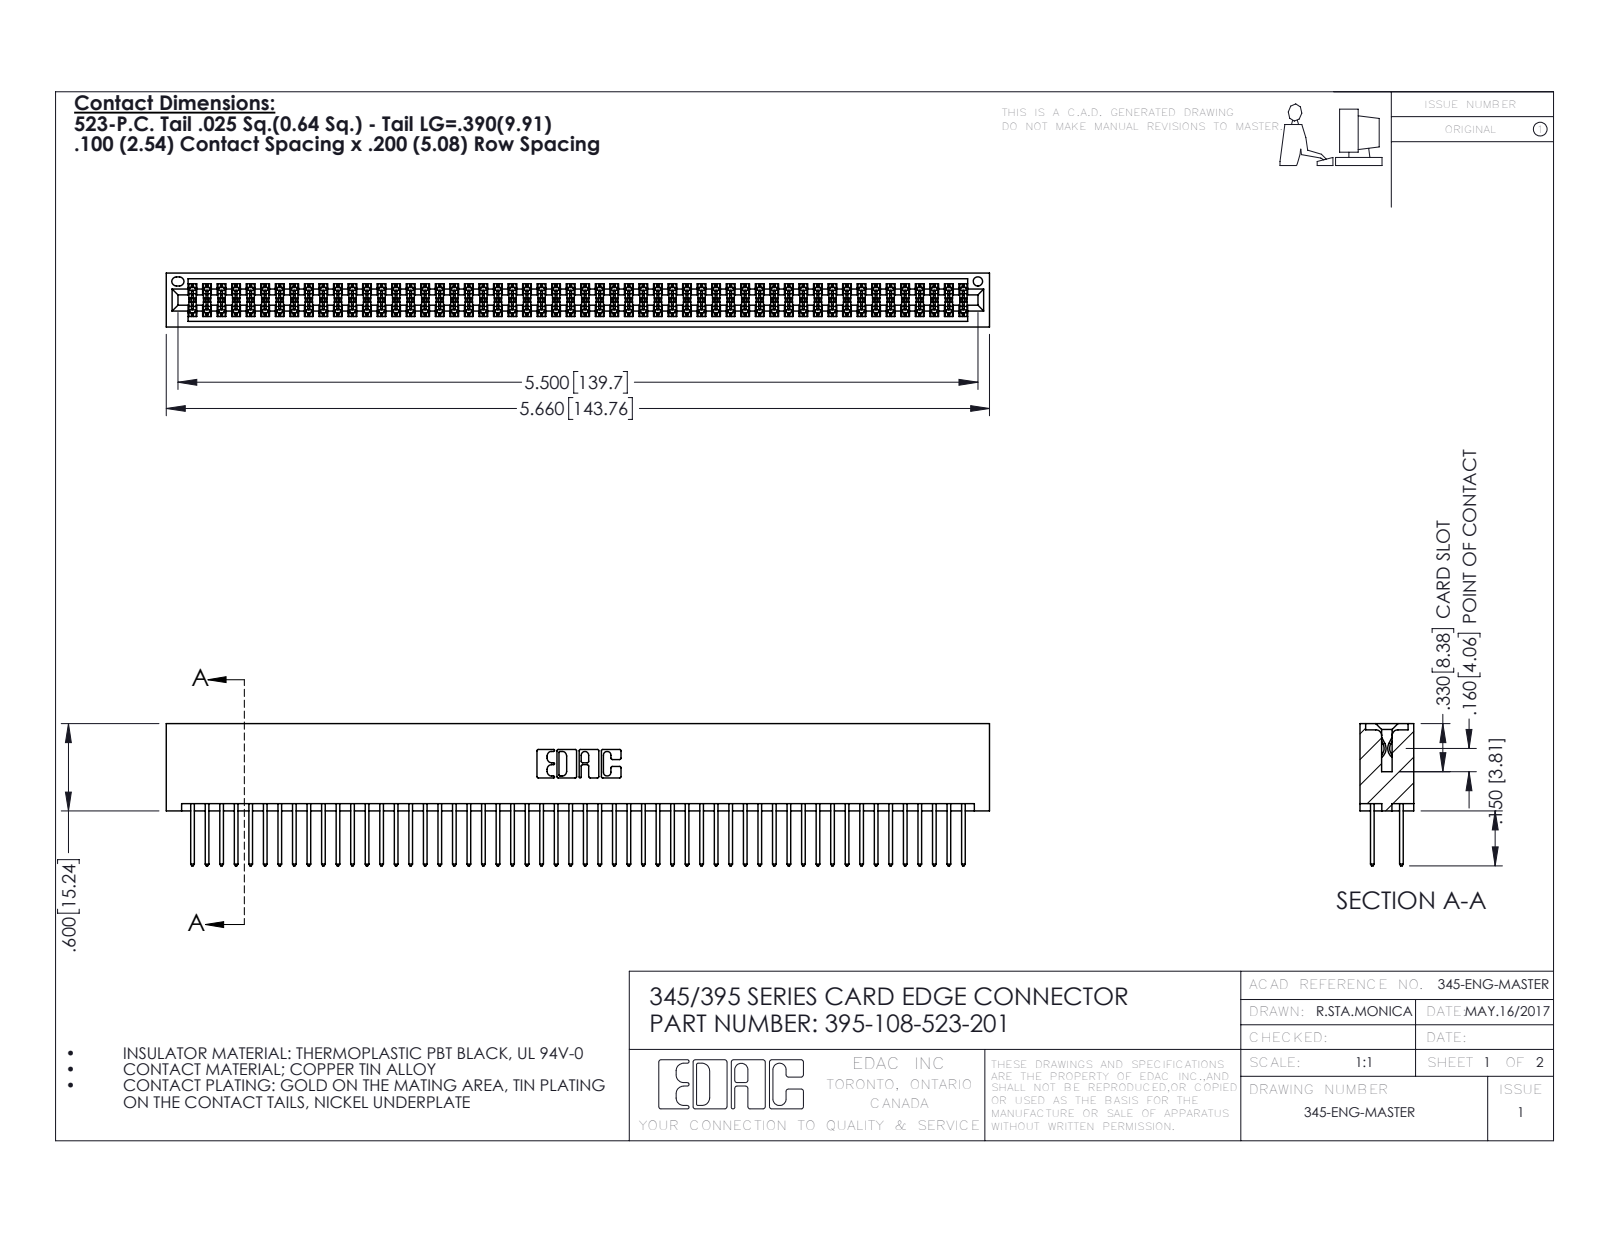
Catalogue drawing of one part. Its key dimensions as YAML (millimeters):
part_name: "345 Part_No Mounting Lugs; 345-292-001_345-293-123; 395-108-523-201"
step_written_by: "SolidWorks 2016 (CONFIG_CONTROL_DESIGN)"
units: millimeters
bodies: {solids: 109, faces: 5518, planar: 3640, cylindrical: 1878, other: 0}
overall_size: [143.8, 24.8, 9.4]
volume: 14900
surface_area: 23570
round_holes:
  - {diameter: 1.6, count: 1}
partial_cylinders:
  - {radius: 0.2, count: 162}
  - {radius: 0.3, count: 108}
  - {radius: 0.3, count: 22}
  - {radius: 0.2, count: 6}
  - {radius: 0.8, count: 6}
  - {radius: 0.7, count: 3}
  - {radius: 0.4, count: 2}
  - {radius: 0.5, count: 2}
face_to_face_distances: [7.6, 1.8, 5.1, 2.5, 6.9, 0.6, 9.4, 5.7, 4.4, 3.8]
